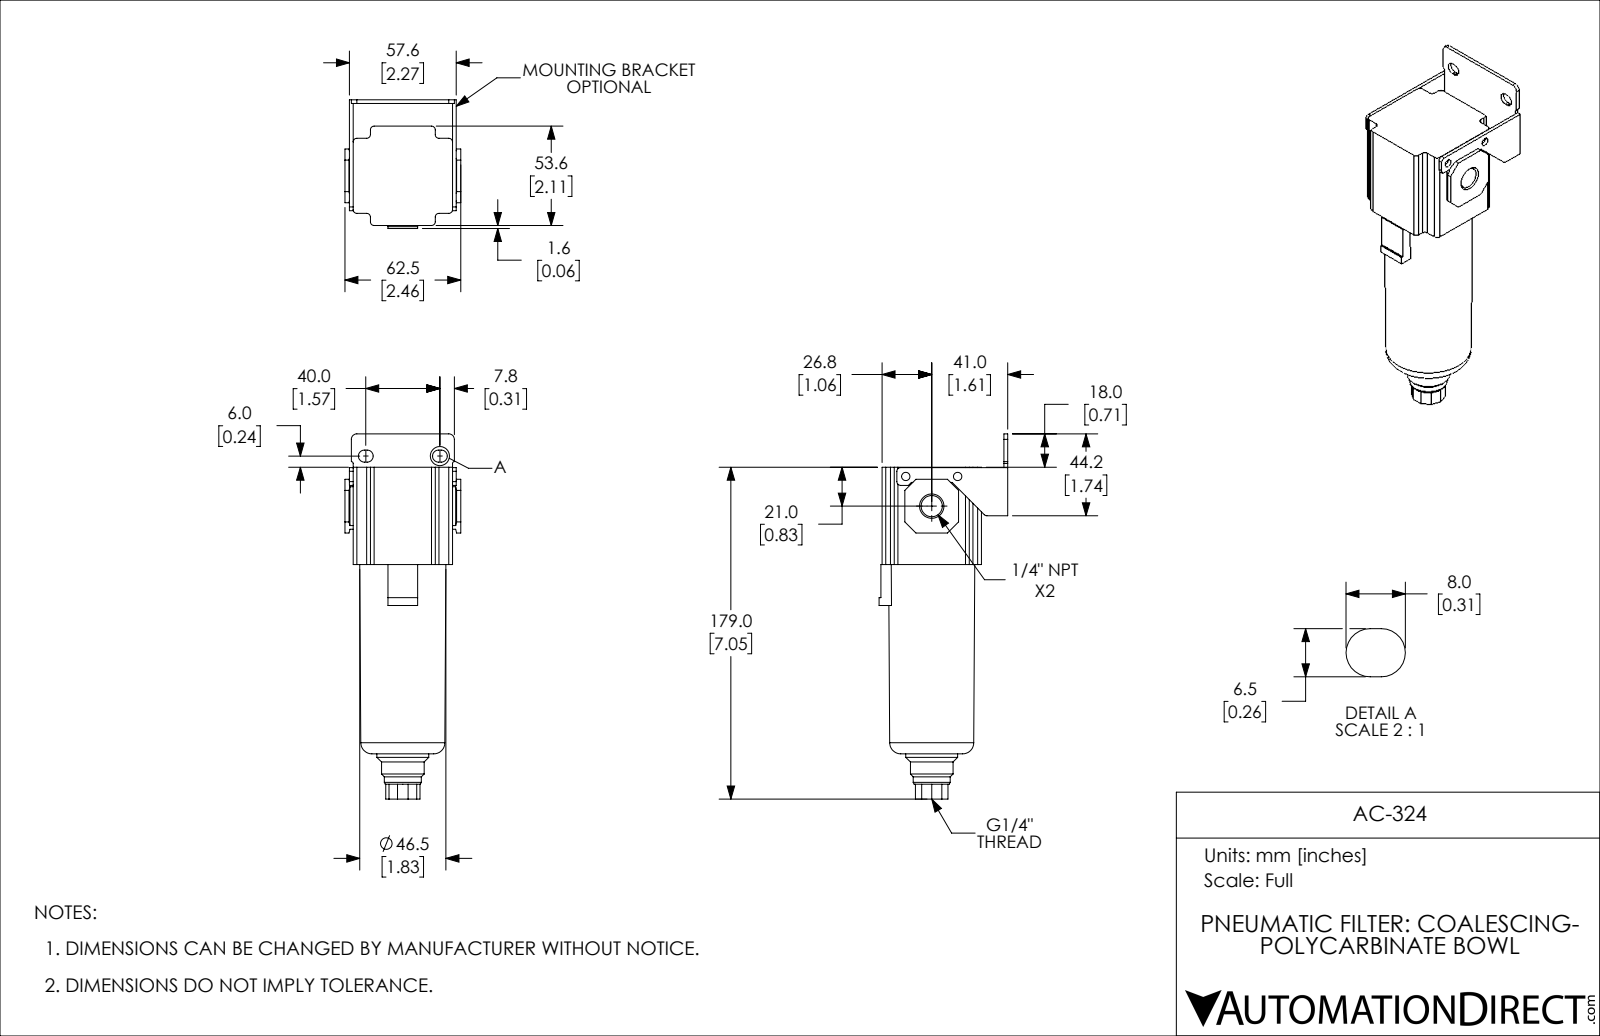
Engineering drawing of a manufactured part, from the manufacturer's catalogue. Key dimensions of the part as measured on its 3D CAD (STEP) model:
Part name (STEP PRODUCT): AC-324
STEP written by: SolidWorks 2018 (AUTOMOTIVE_DESIGN)
Units: inches
Bodies: 1 solid, 173 faces (109 planar, 48 cylindrical, 16 other)
Overall size (bounding box): 7.756 × 2.733 × 2.461
Volume: 20 in³ · Surface area: 65.25 in²
Round holes (diameter × count): ⌀0.177 ×2, ⌀0.451 ×2
Round bosses / shafts (diameter × count): ⌀1.102 ×1, ⌀0.906 ×1, ⌀0.787 ×1
Partial cylindrical surfaces — rounded edges, fillets, slot ends (radius × count): R0.079 ×15, R0.128 ×4, R0.039 ×2, R0.118 ×2
Main face-to-face distances: 0.079, 2.11, 2.189, 0.559, 2.669, 0.48, 2.591, 0.096, 0.175, 2.285
Hole centre spacings: 0.837, 1.102
